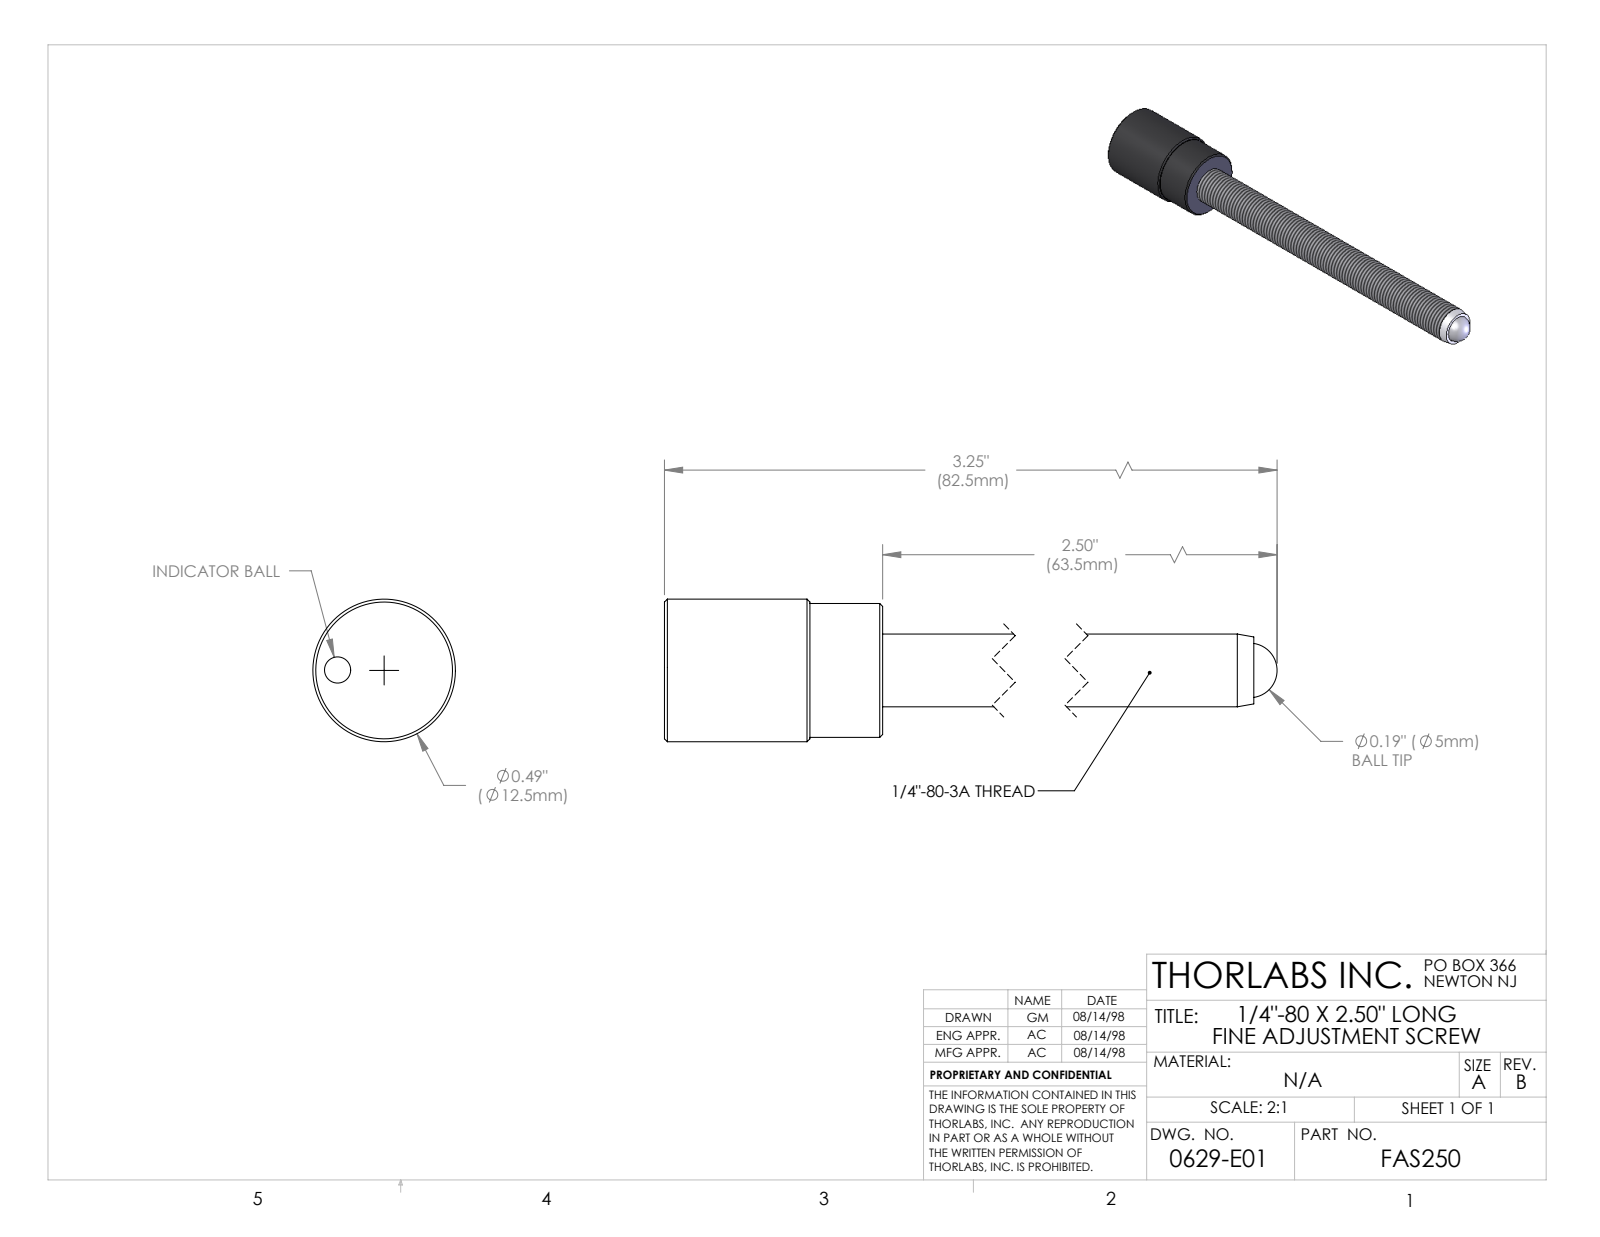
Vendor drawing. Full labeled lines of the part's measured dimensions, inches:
Part name (STEP PRODUCT): 0629-E0W
STEP written by: SolidWorks 2007 (AUTOMOTIVE_DESIGN)
Units: inches
Bodies: 4 solids, 40 faces (8 planar, 14 cylindrical, 18 other)
Overall size (bounding box): 3.25 × 0.49 × 0.49
Volume: 0.257 in³ · Surface area: 4.444 in²
Round holes (diameter × count): ⌀0.09 ×1, ⌀0.188 ×1, ⌀0.234 ×1, ⌀0.248 ×1
Round bosses / shafts (diameter × count): ⌀0.49 ×1, ⌀0.46 ×1, ⌀0.25 ×1
Main face-to-face distances: 0.75, 0.25, 0.5, 3.17, 2.92, 2.42, 2.67, 0.09, 0.16, 0.41
Hole centre spacings: 0.16
